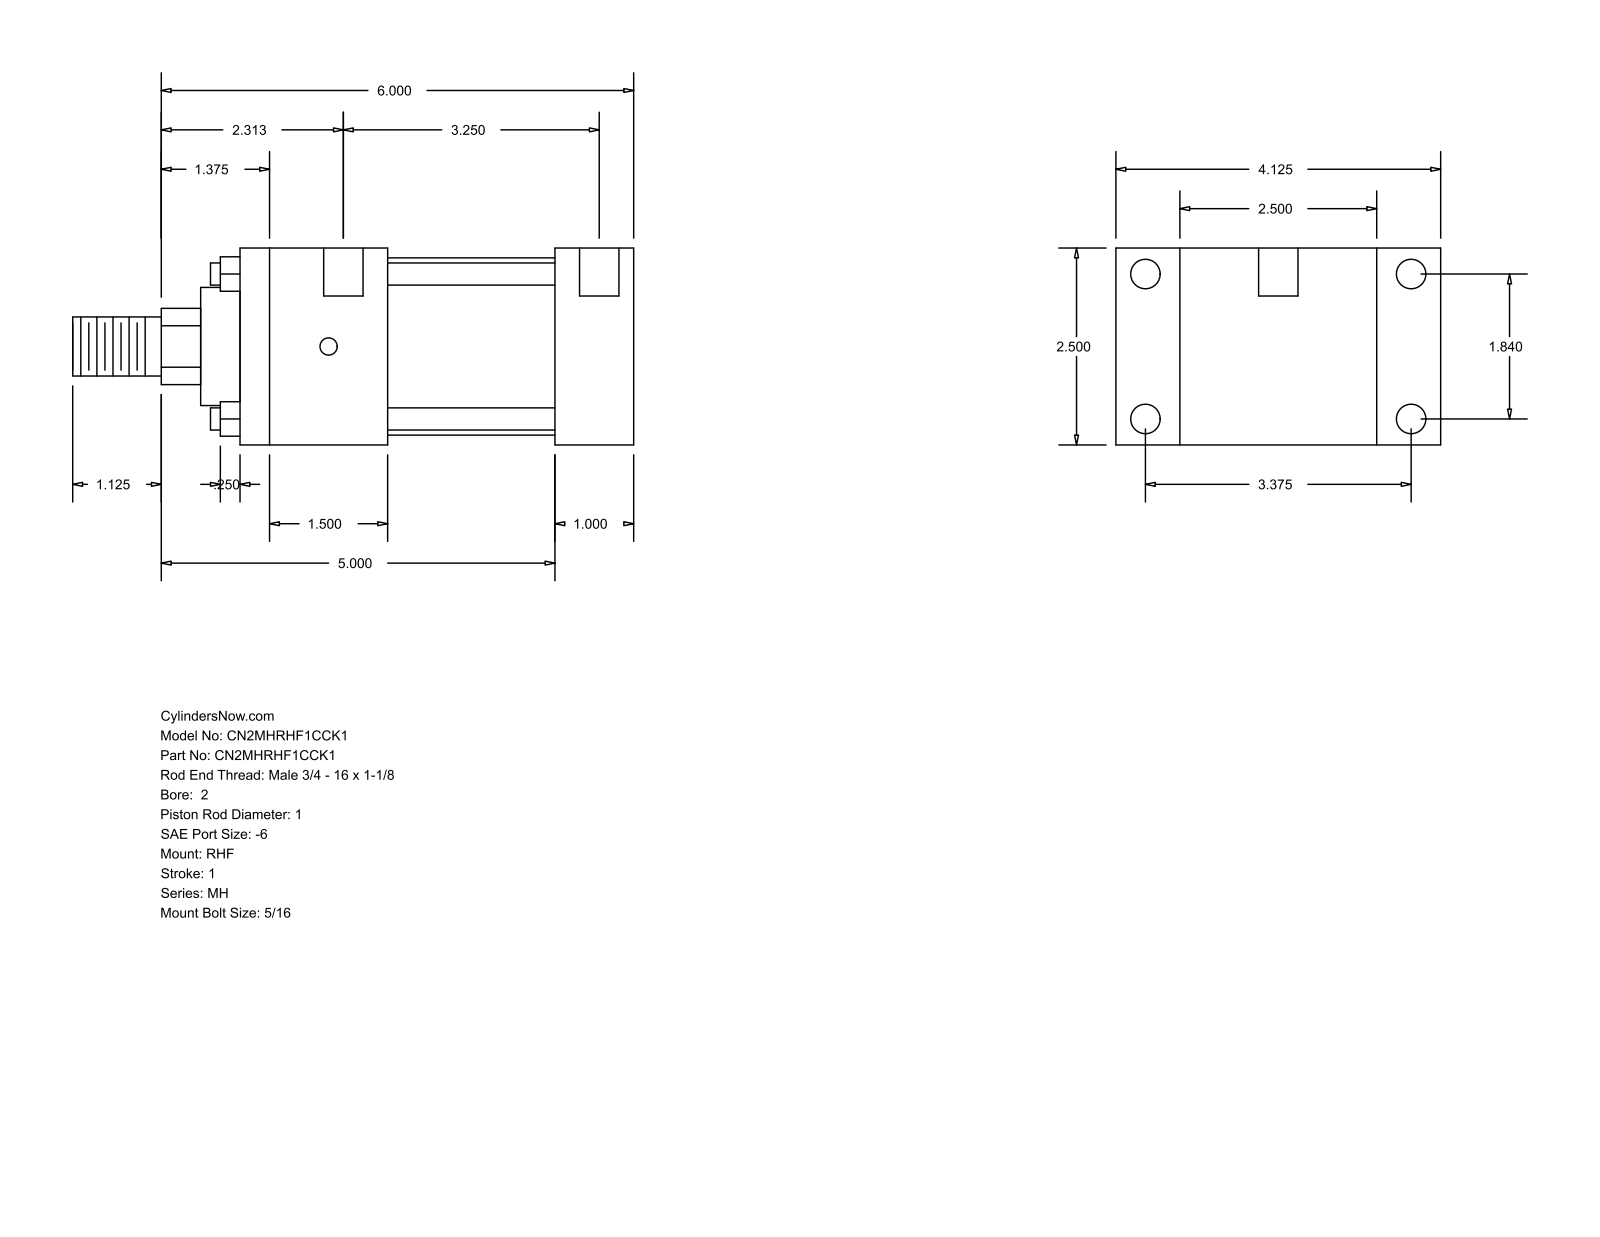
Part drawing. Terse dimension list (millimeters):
name: MH_RHF__0200_1
written by: GSSL Pune (CONFIG_CONTROL_DESIGN)
unit: mm
bodies: 0 solids, 88 faces (60 planar, 28 cylindrical, 0 other)
size: 180.97 × 104.78 × 63.5
holes: 4× ⌀5.56, 4× ⌀9.53, 2× ⌀12.7
bosses: 4× ⌀7.14, 1× ⌀57.15, 1× ⌀38.1, 1× ⌀25.4, 1× ⌀19.05
rounds: 1× R12.29
face distances: 63.5, 25.4, 20.64, 84.14, 101.6, 127, 53.97, 104.78, 47.63, 79.37
hole spacings: 85.72, 46.74, 90.48, 97.63, 3.17, 4.76, 82.55, 87.31
